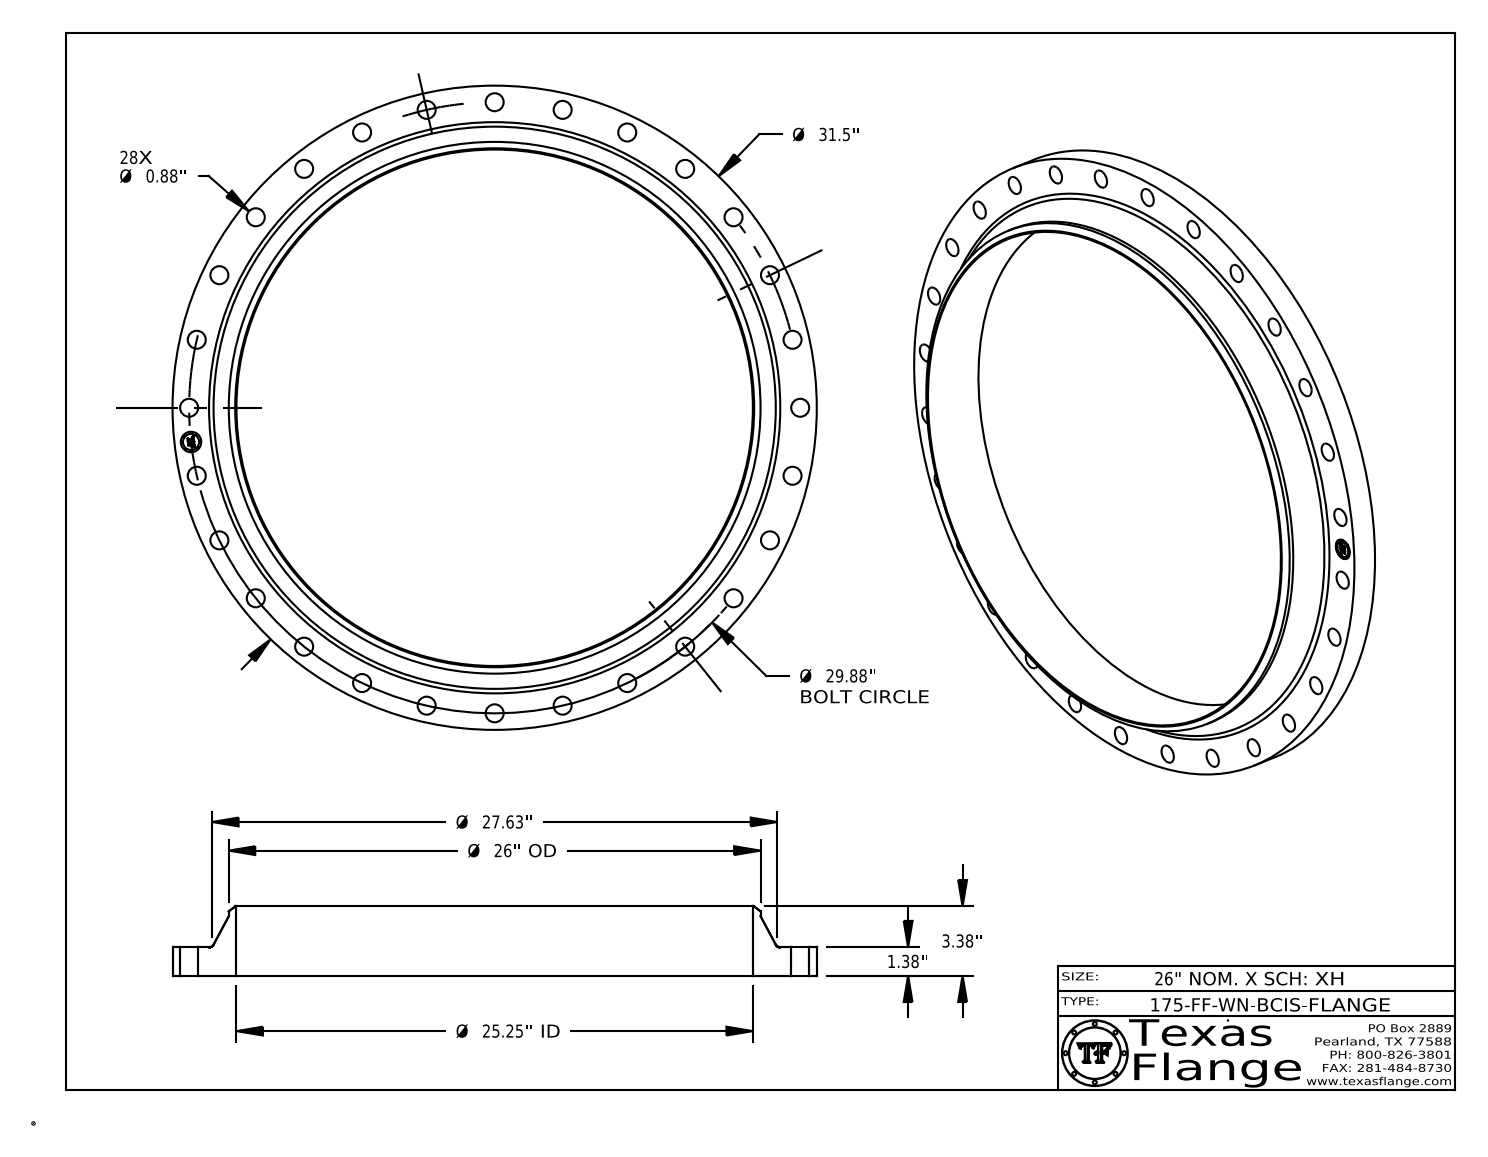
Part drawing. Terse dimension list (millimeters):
name: 175-FF-WN, BCIS
written by: CATIA V5 STEP AP214 (AUTOMOTIVE_DESIGN)
unit: mm
bodies: 1 solid, 456 faces (368 planar, 82 cylindrical, 6 other)
size: 800.1 × 800.1 × 85.9
volume: 7 708 000 mm³; area: 732 300 mm²
holes: 28× ⌀22.4, 1× ⌀25.4, 1× ⌀641.4
bosses: 8× ⌀1.5, 1× ⌀800.1, 1× ⌀660.4, 1× ⌀20
face distances: 35.1, 85.9, 50.8, 0.4, 34.7, 51.2, 7.6, 7.4, 1.4, 4.9
hole spacings: 250.7, 403.8, 473.2, 379.5, 168.9, 329.3, 85, 536.7
